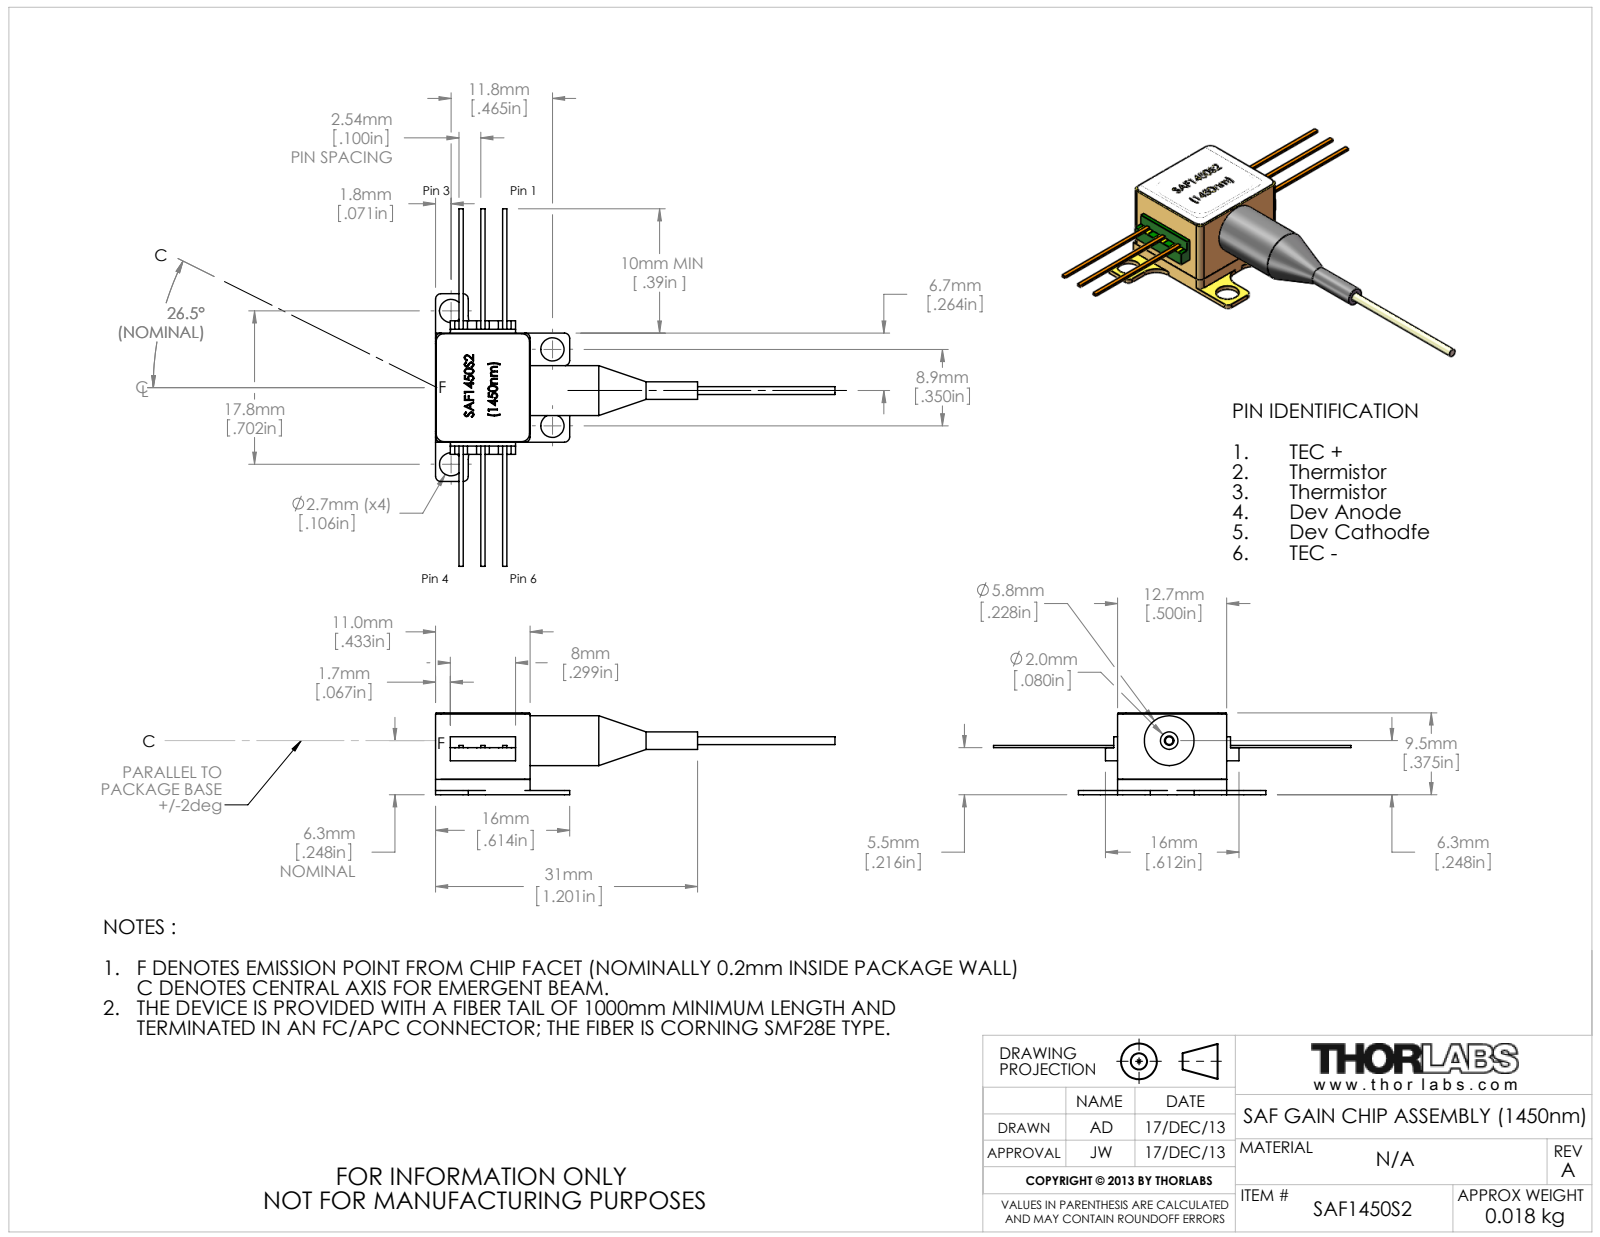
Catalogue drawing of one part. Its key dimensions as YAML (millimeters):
part_name: "QTN006404-E0W"
step_written_by: "SolidWorks 2012 (AUTOMOTIVE_DESIGN)"
units: millimeters
bodies: {solids: 15, faces: 491, planar: 322, cylindrical: 70, other: 99}
overall_size: [46.5, 41.6, 9.53]
volume: 931
surface_area: 2425
round_holes:
  - {diameter: 2.7, count: 4}
  - {diameter: 1.1, count: 1}
  - {diameter: 2.08, count: 1}
  - {diameter: 3.18, count: 1}
  - {diameter: 4.1, count: 1}
round_bosses_or_shafts:
  - {diameter: 5.8, count: 1}
  - {diameter: 3.45, count: 1}
  - {diameter: 2.04, count: 1}
  - {diameter: 0.9, count: 1}
partial_cylinders:
  - {radius: 0.6, count: 12}
  - {radius: 1, count: 10}
  - {radius: 0.13, count: 4}
  - {radius: 0.3, count: 4}
  - {radius: 0.9, count: 4}
  - {radius: 1.85, count: 4}
  - {radius: 2, count: 4}
face_to_face_distances: [1, 1.6, 9.52, 7.92, 7.6, 9.4, 7.8, 1.8, 1.45, 11.7]
hole_center_spacings: [12.62, 17.83, 8.9, 17.84]
